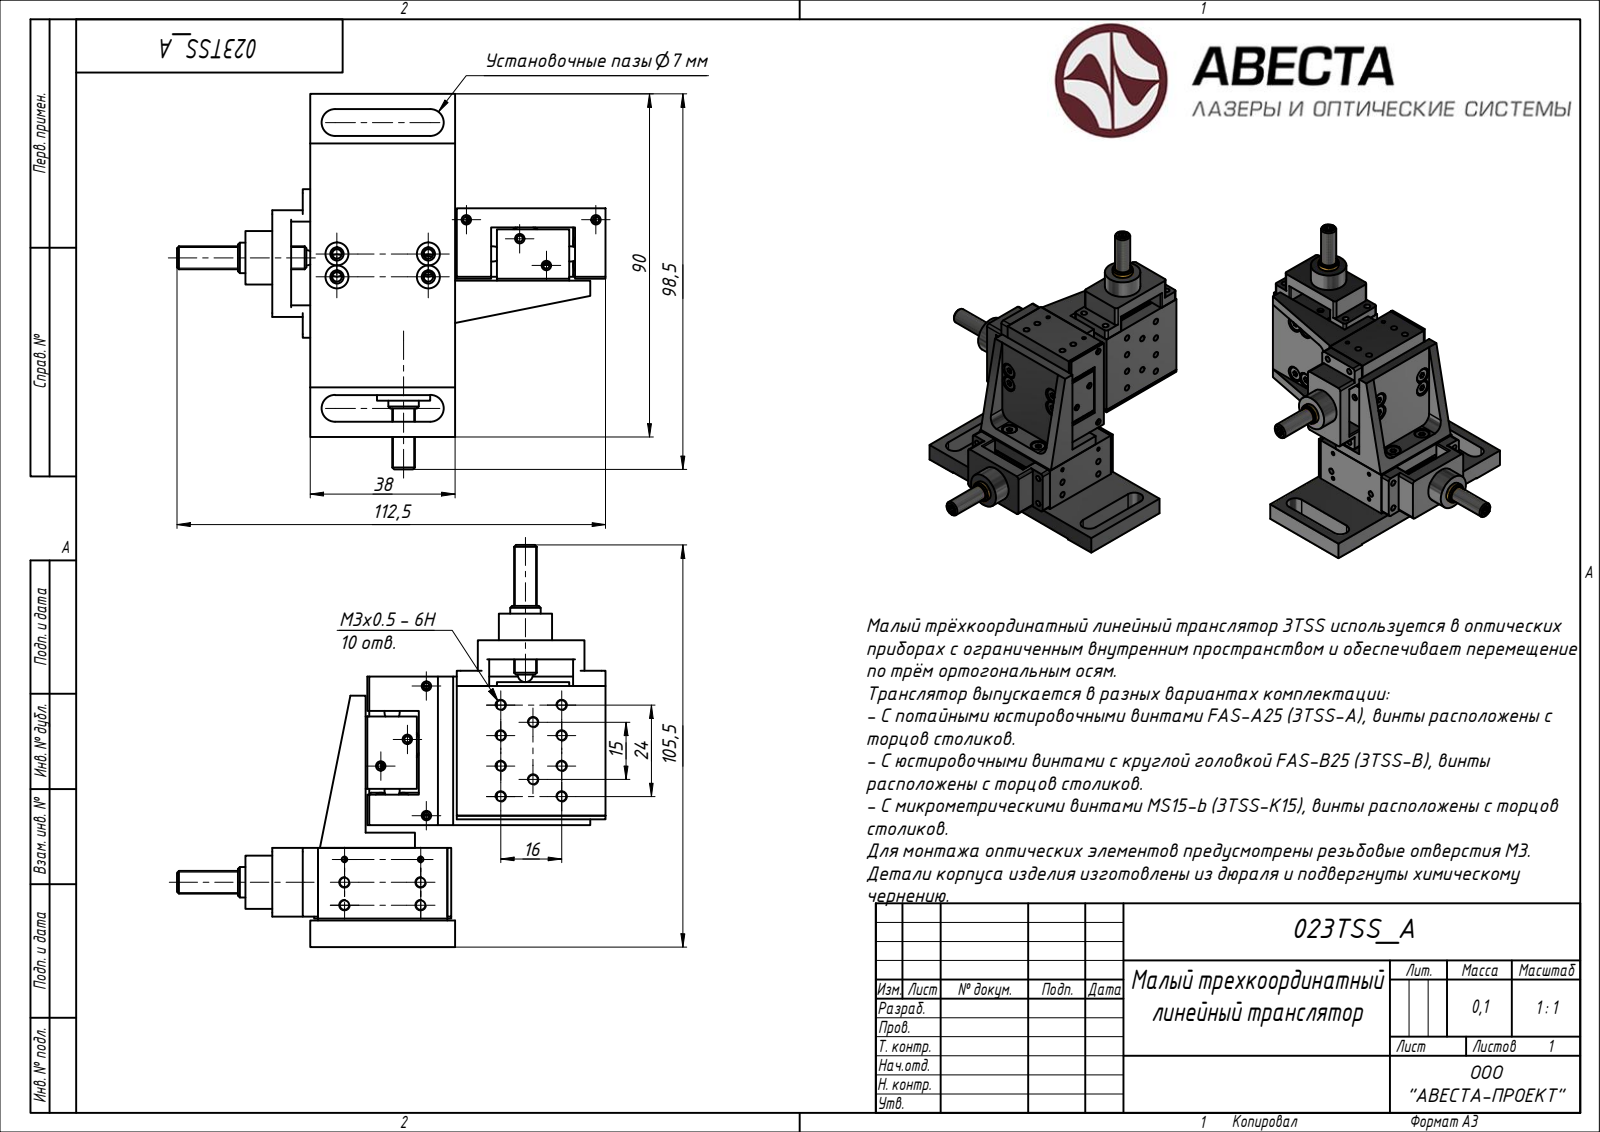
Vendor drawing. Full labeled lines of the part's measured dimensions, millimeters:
STEP written by: ST-DEVELOPER v15 (AUTOMOTIVE_DESIGN)
Units: millimetres
Bodies: 59 solids, 1640 faces (0 planar, 0 cylindrical, 1640 other)
Overall size (bounding box): 112.5 × 105.5 × 99.22
